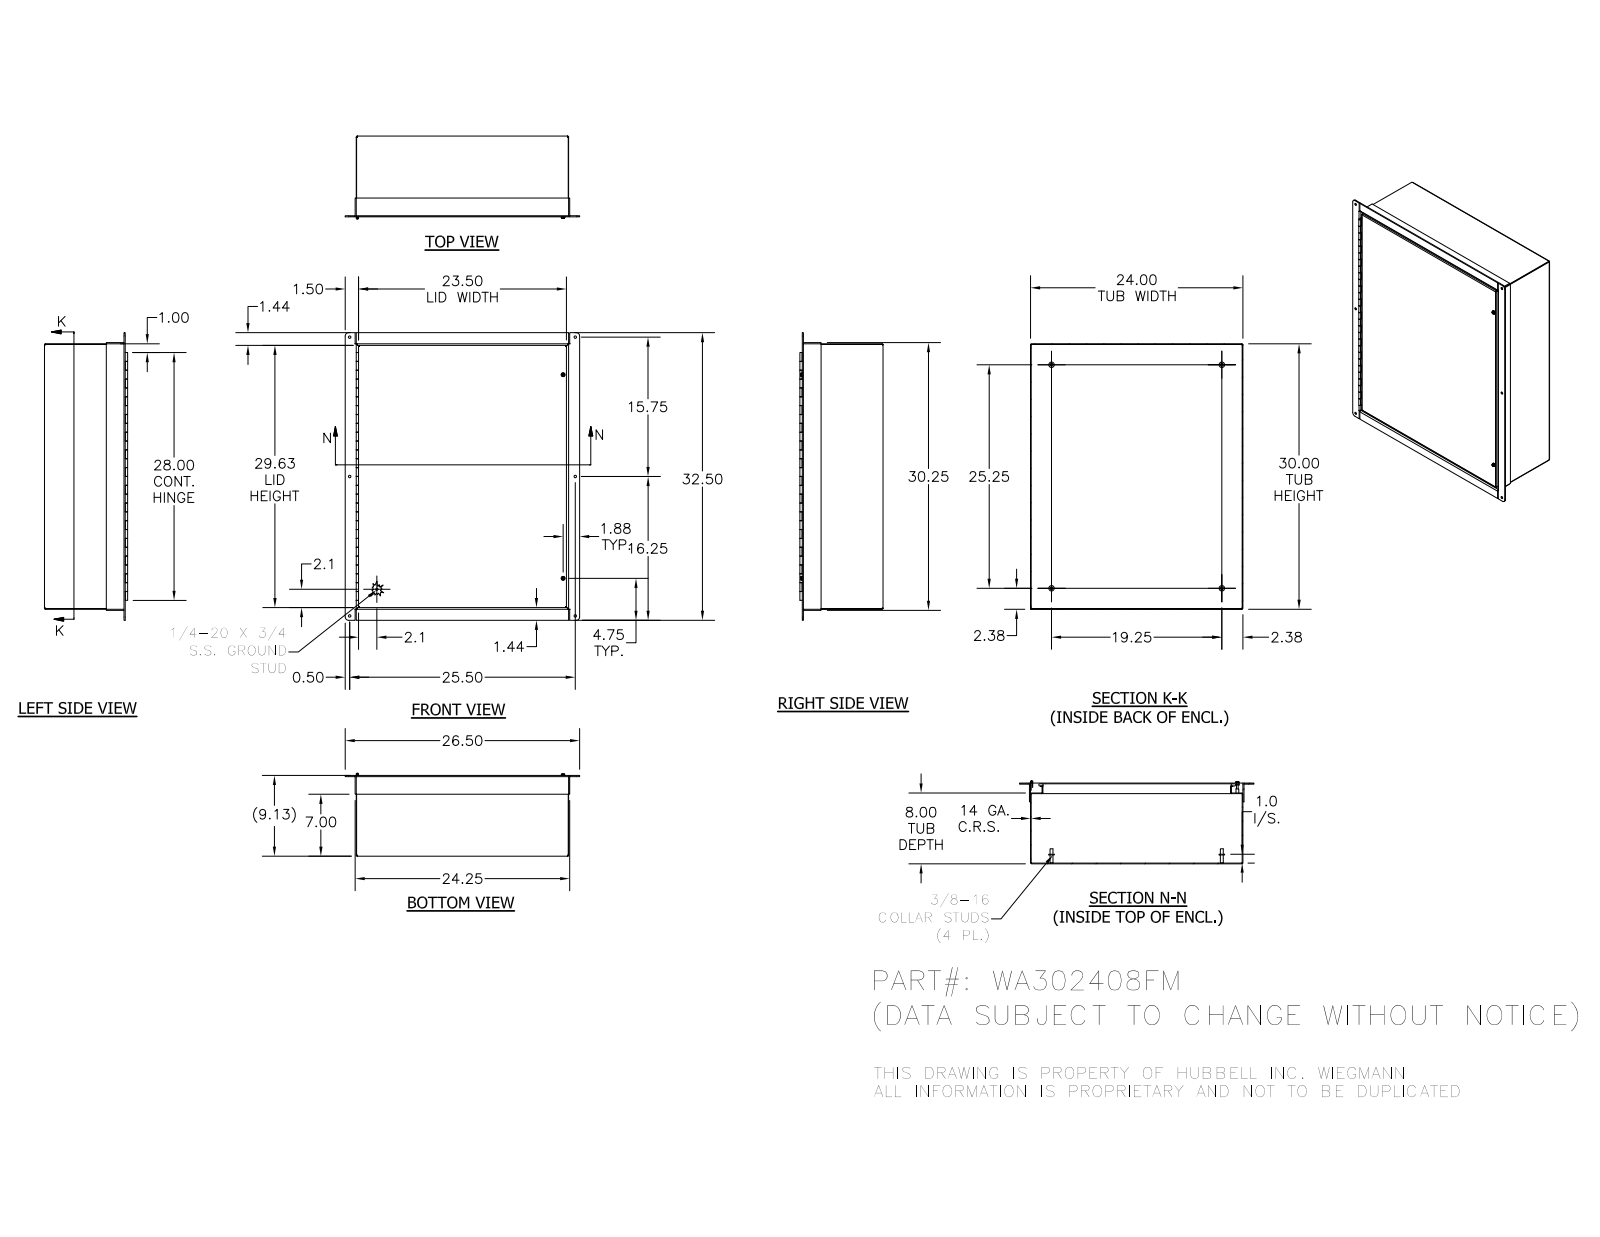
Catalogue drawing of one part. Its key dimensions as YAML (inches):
part_name: "WA302408FMBKP; WA3024FMLID; 388116; H6010102T (+8 more)"
step_written_by: "Autodesk Inventor 2016 (AUTOMOTIVE_DESIGN)"
units: inches
bodies: {solids: 23, faces: 684, planar: 431, cylindrical: 182, other: 71}
overall_size: [32.5, 26.5, 9.4]
volume: 248.9
surface_area: 6144
round_holes:
  - {diameter: 0.281, count: 8}
  - {diameter: 0.375, count: 5}
  - {diameter: 0.156, count: 2}
  - {diameter: 0.188, count: 2}
  - {diameter: 0.278, count: 2}
  - {diameter: 0.125, count: 1}
round_bosses_or_shafts:
  - {diameter: 0.625, count: 4}
  - {diameter: 0.33, count: 4}
  - {diameter: 0.453, count: 2}
  - {diameter: 0.437, count: 2}
  - {diameter: 0.414, count: 2}
  - {diameter: 0.313, count: 2}
  - {diameter: 0.25, count: 2}
  - {diameter: 0.19, count: 2}
partial_cylinders:
  - {radius: 0.031, count: 24}
  - {radius: 0.105, count: 20}
  - {radius: 0.07, count: 8}
  - {radius: 0.125, count: 8}
  - {radius: 0.156, count: 4}
  - {radius: 0.375, count: 4}
  - {radius: 0.089, count: 2}
face_to_face_distances: [0.074, 9.041, 8.967, 9.115, 23.926, 29.926, 24, 0.125, 7.926, 1.115]
hole_center_spacings: [4.467, 6.75, 11.582, 15.75, 23, 27.285, 29.972, 13.5]
